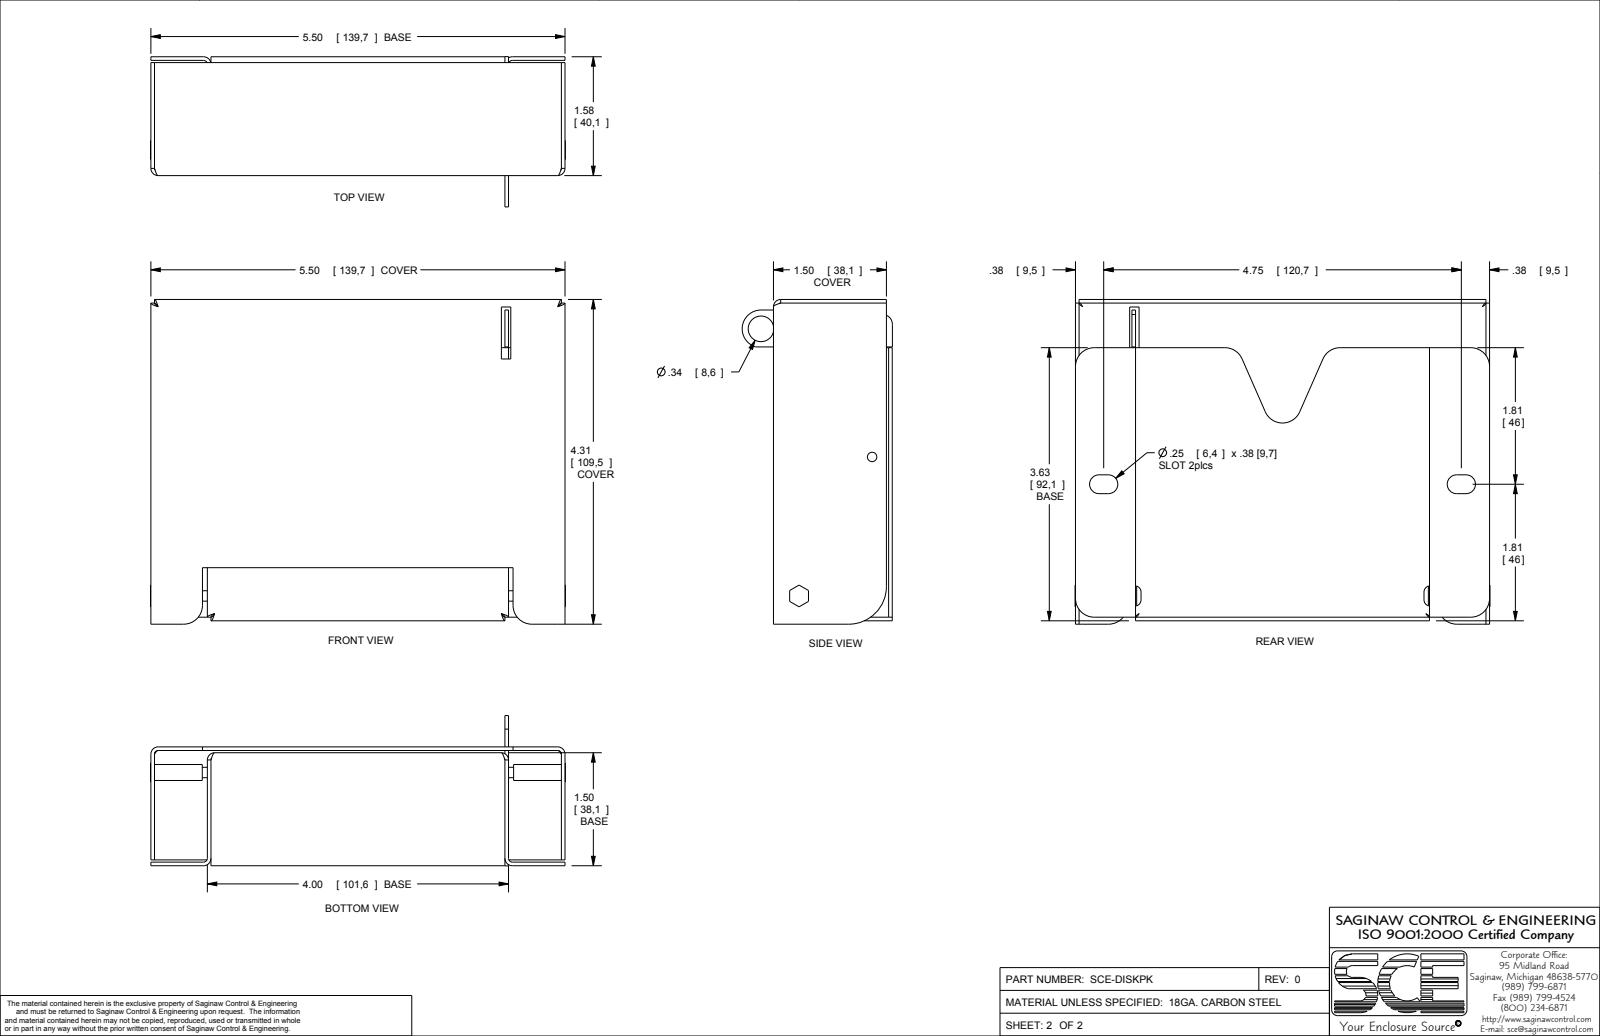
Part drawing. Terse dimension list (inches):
name: SCE-DISKPK
written by: SolidWorks 2019 (CONFIG_CONTROL_DESIGN)
unit: in
bodies: 0 solids, 198 faces (106 planar, 64 cylindrical, 28 other)
size: 5.51 × 4.31 × 1.995
holes: 1× ⌀0.125, 1× ⌀0.138, 1× ⌀0.213, 1× ⌀0.34
bosses: 1× ⌀0.262, 1× ⌀0.212
rounds: 10× R0.25, 6× R0.048, 6× R0.096, 4× R0.125, 2× R0.05, 2× R0.08, 2× R0.098, 1× R0.13
face distances: 0.048, 0.078, 0.75, 4.702, 0.03, 0.126, 5.452, 4.217, 1.452, 0.798
hole spacings: 2.085, 2.251, 3.581
